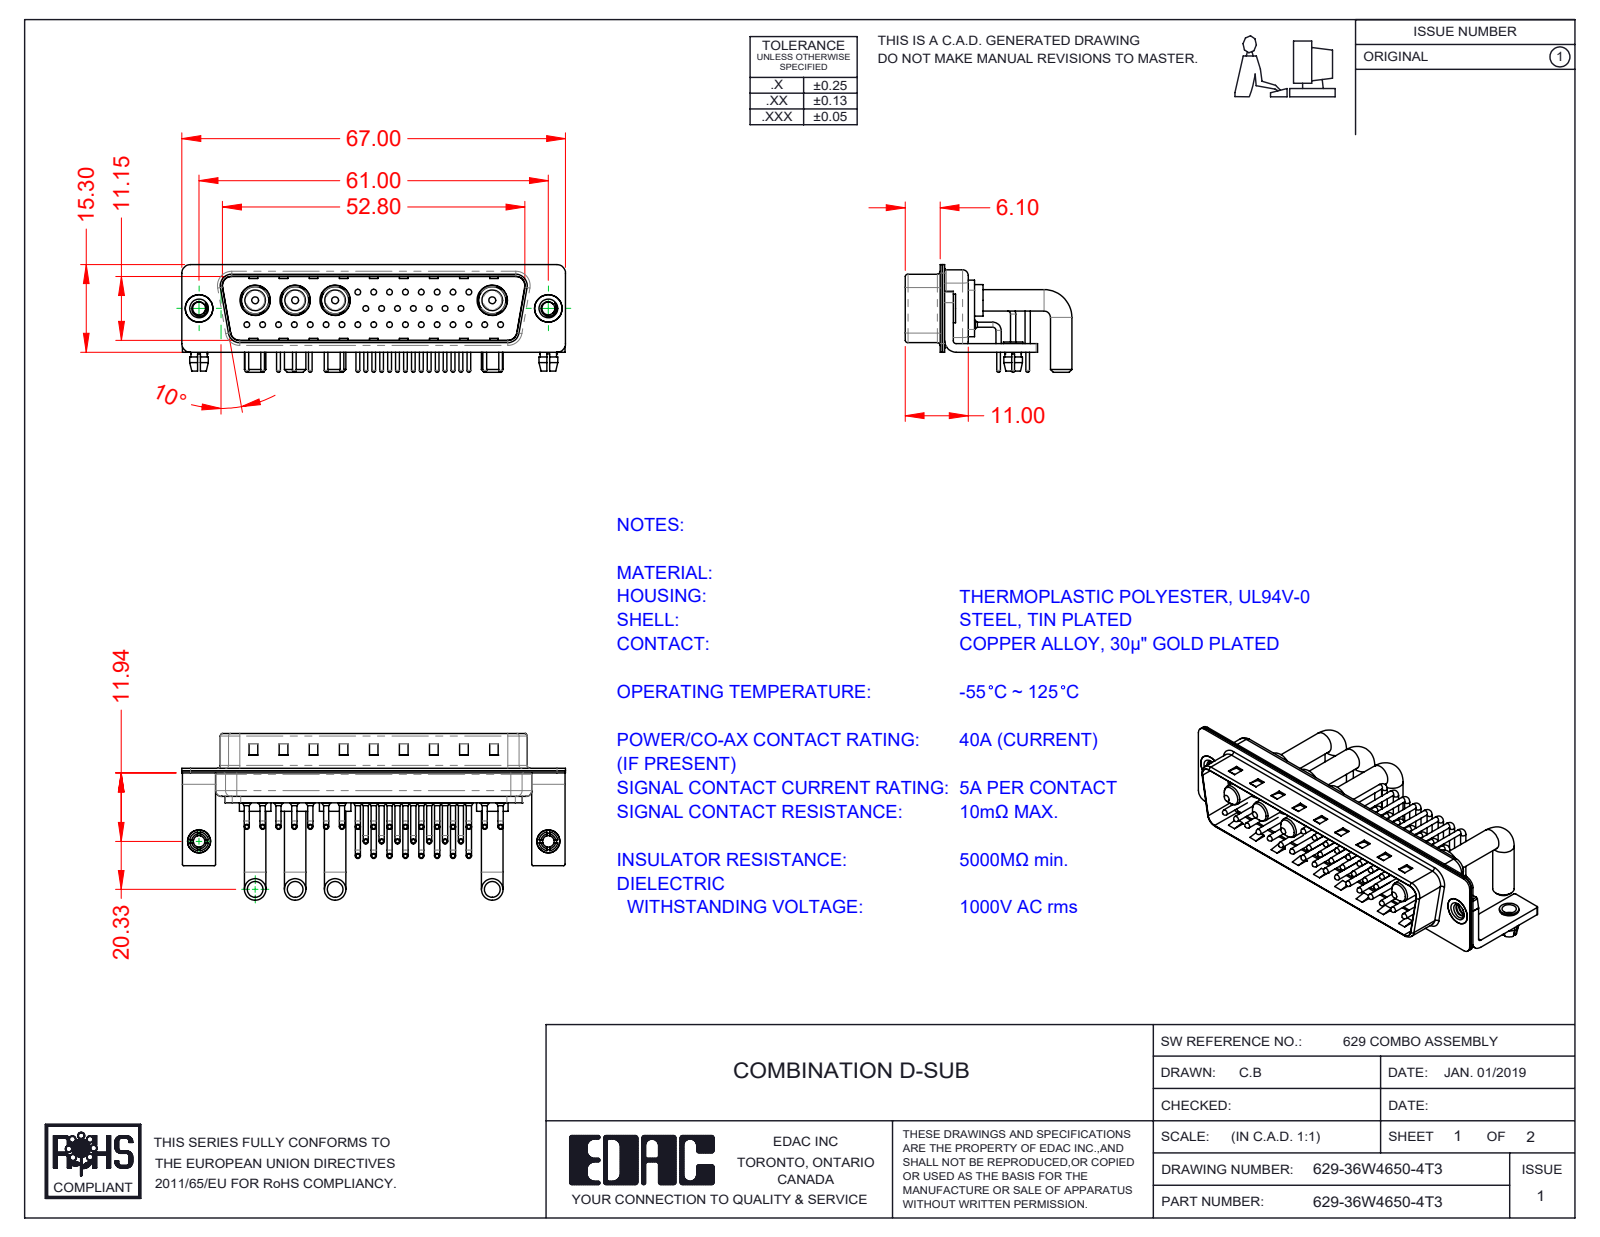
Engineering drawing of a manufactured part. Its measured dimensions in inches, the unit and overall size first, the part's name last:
Units: inches
Overall size (bounding box): 2.638 × 1.146 × 0.74
Round holes (diameter × count): ⌀0.079 ×34, ⌀0.03 ×32, ⌀0.063 ×32, ⌀0.191 ×4, ⌀0.209 ×4, ⌀0.089 ×2, ⌀0.098 ×2, ⌀0.126 ×2, ⌀0.157 ×2, ⌀0.189 ×2
Round bosses / shafts (diameter × count): ⌀0.035 ×64, ⌀0.059 ×32, ⌀0.039 ×32, ⌀0.026 ×32, ⌀0.148 ×8, ⌀0.217 ×4, ⌀0.205 ×4, ⌀0.187 ×4
Partial cylindrical surfaces — rounded edges, fillets, slot ends (radius × count): R0.04 ×32, R0.01 ×16, R0.059 ×16, R0.079 ×13, R0.02 ×9, R0.063 ×8, R0.024 ×4, R0.026 ×4
Main face-to-face distances: 0.016, 0.059, 0.455, 0.22, 0.205, 0.031, 0.236, 0.075, 0.031, 0.043
Hole centre spacings: 0.109, 0.218, 0.124, 0.327, 0.436, 0.545, 0.654, 0.763
Volume: 0.394 in³ · Surface area: 21.47 in²
Bodies: 49 solids, 4236 faces (2359 planar, 1427 cylindrical, 450 other)
Part name (STEP PRODUCT): 629Combo Board Lock_50 Contacts; Power Pin_Ext 40A RA 50; 629Combo Threaded Rivet_3; 629Combo Contact Row 2_50 Contacts (+7 more)
STEP written by: SolidWorks 2020 (CONFIG_CONTROL_DESIGN)
